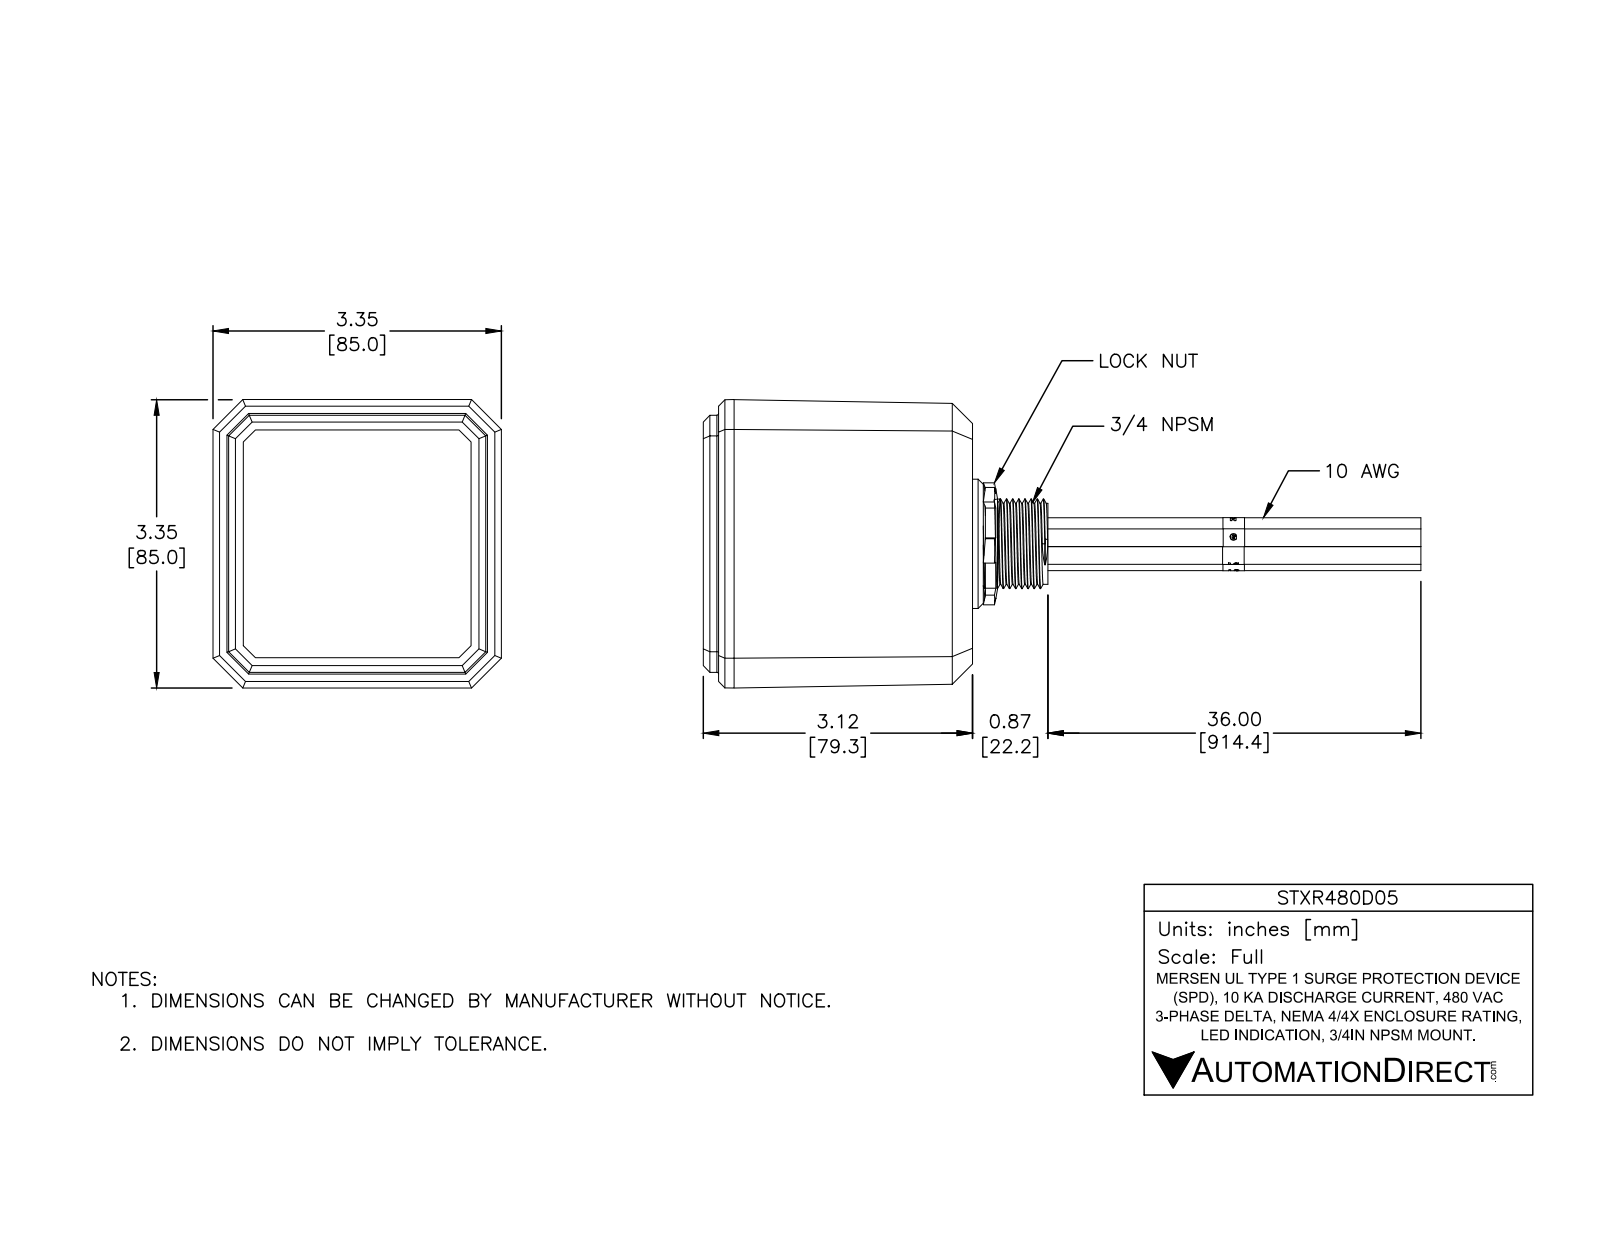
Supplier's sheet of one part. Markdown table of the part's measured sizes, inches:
| quantity | value |
| --- | --- |
| part name | STXR480D05 |
| STEP written by | SolidWorks 2016 (AUTOMOTIVE_DESIGN) |
| units | inches |
| bodies | 7 solids, 510 faces (315 planar, 115 cylindrical, 80 other) |
| overall size | 8.327 × 3.347 × 3.347 |
| volume | 8.231 in³ |
| surface area | 144.4 in² |
| round holes (diameter × count) | 1 × 1 |
| round bosses / shafts (diameter × count) | 0.205 × 12, 0.205 × 3, 0.145 × 3, 1.5 × 1, 0.94 × 1, 0.145 × 1 |
| partial cylindrical surfaces (radius × count) | 0.015 × 16, 0.02 × 8, 0.1 × 8, 0.04 × 4, 0.31 × 1, 0.639 × 1 |
| main face-to-face distances | 0.125, 0.125, 0.12, 2.989, 3.109, 2.864, 2.984, 2.766, 2.641, 0.223 |
